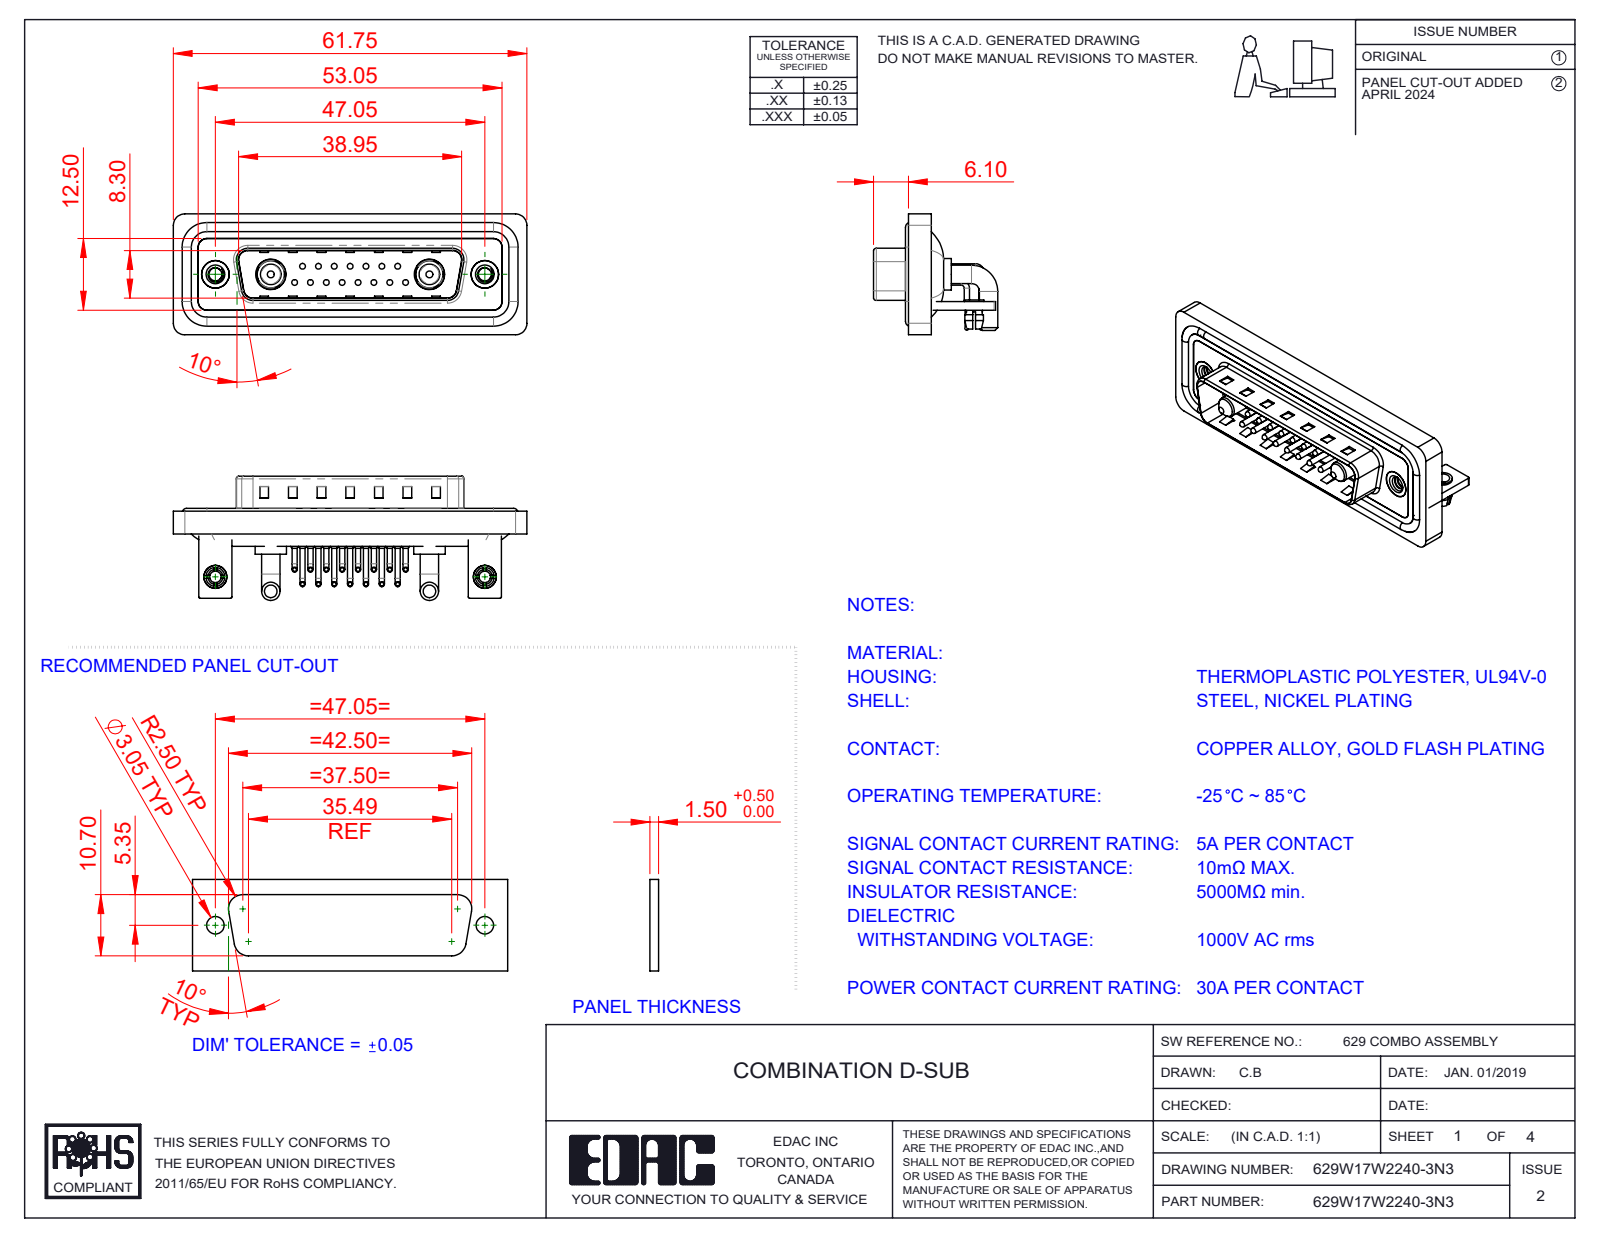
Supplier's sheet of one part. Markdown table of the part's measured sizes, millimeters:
| quantity | value |
| --- | --- |
| part name | 629Combo Stabilizer Bracket; 629Combo Housing_17W2; 629W17W2140-3N3; 629Combo Board Lock (+7 more) |
| STEP written by | SolidWorks 2023 (CONFIG_CONTROL_DESIGN) |
| units | millimeters |
| bodies | 30 solids, 2351 faces (1257 planar, 820 cylindrical, 274 other) |
| overall size | 61.75 × 21.7 × 21.1 |
| volume | 7 882 mm³ |
| surface area | 13 435 mm² |
| round holes (diameter × count) | 2 × 17, 0.75 × 15, 1.6 × 15, 2.26 × 2, 2.5 × 2, 3.2 × 2, 4 × 2, 4.8 × 2, 4.85 × 2, 5 × 2, 5.3 × 2 |
| round bosses / shafts (diameter × count) | 0.9 × 30, 1.5 × 15, 1 × 15, 0.65 × 15, 3.2 × 4, 1.6 × 4, 5.5 × 2, 5.2 × 2 |
| partial cylindrical surfaces (radius × count) | 2 × 19, 1.5 × 18, 0.25 × 16, 1.01 × 15, 0.5 × 9, 1.6 × 8, 0.6 × 4, 0.65 × 4 |
| main face-to-face distances | 0.4, 0.8, 1.5, 2.1, 2.9, 1.1, 4.1, 1.6, 4.5, 3.7 |
| hole center spacings | 3.16, 2.77, 5.54, 8.31, 5.04, 7.49, 11.08, 5.03 |
